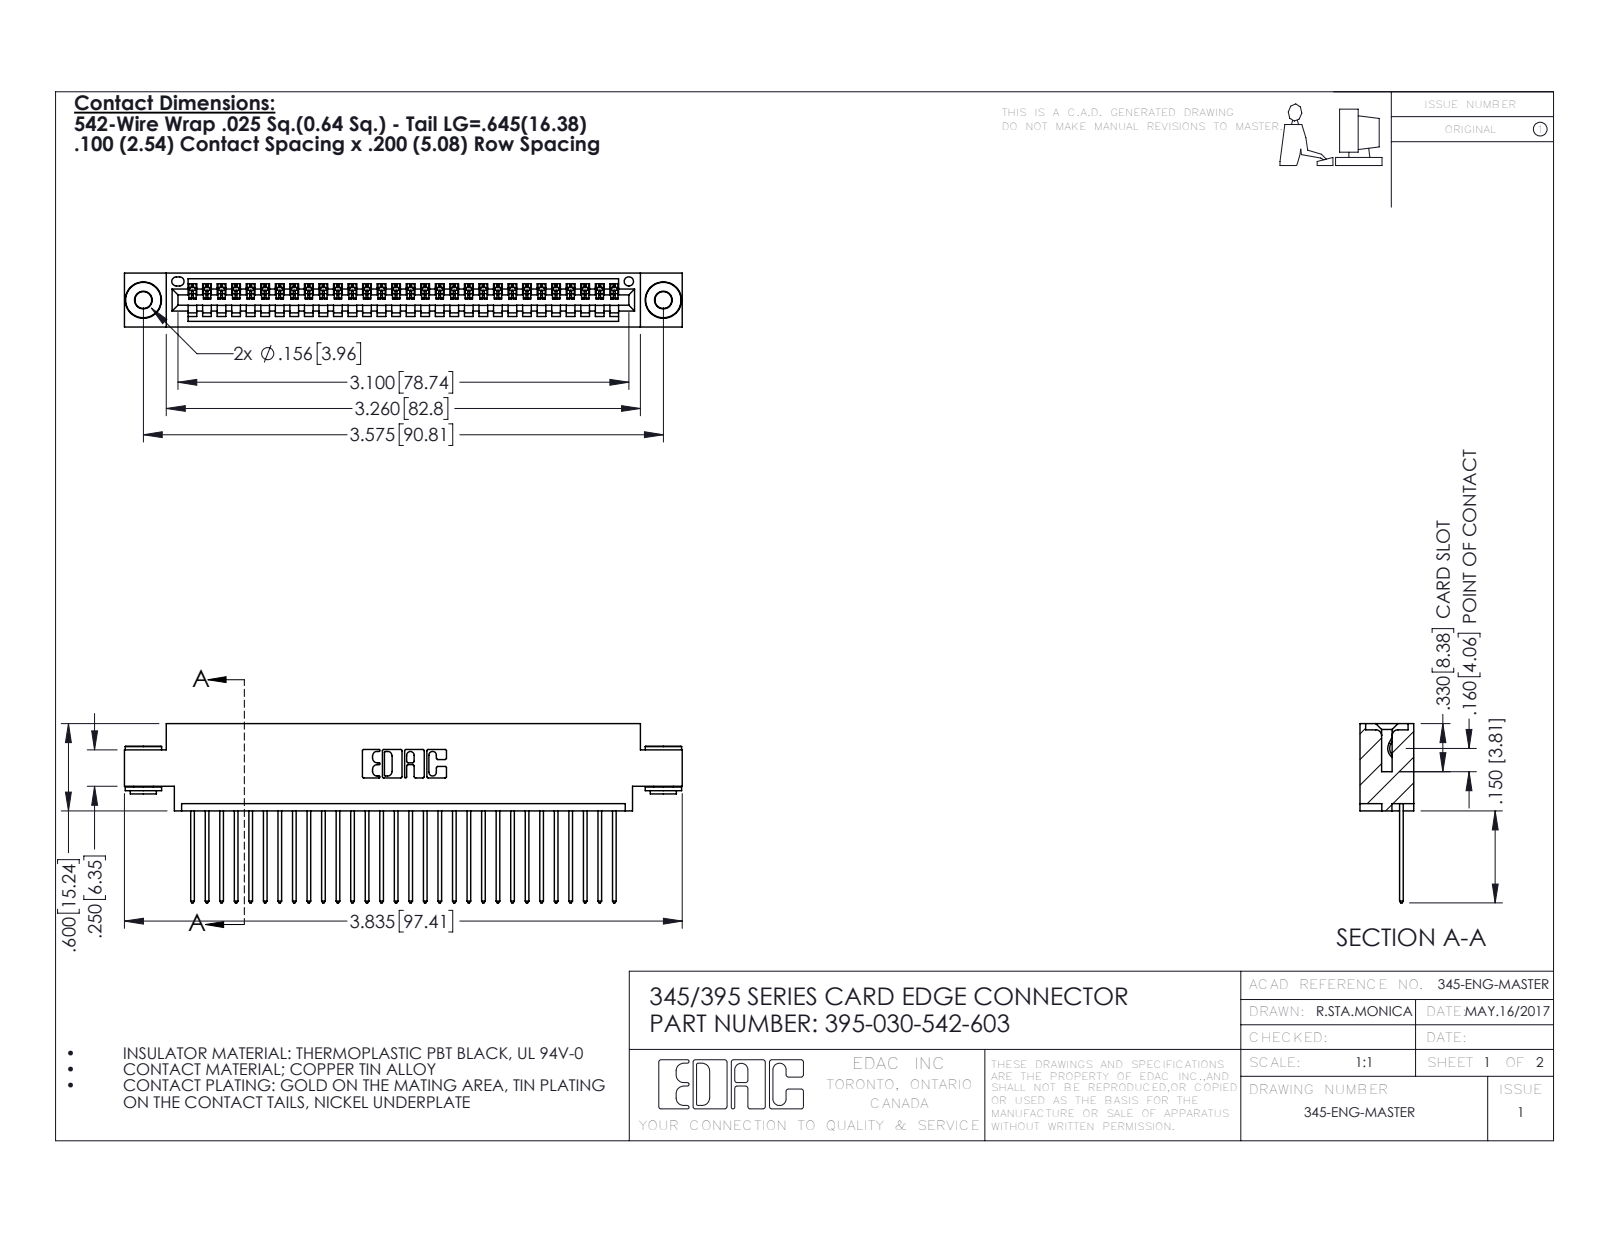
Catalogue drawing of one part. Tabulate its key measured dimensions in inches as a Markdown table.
| quantity | value |
| --- | --- |
| part name | 345-250-002_345-250-002-102; 345 Part_0.170 Offset - 0.156 Dia-TH; 345-292-001_345-293-142; 395-030-542-603 |
| STEP written by | SolidWorks 2016 (CONFIG_CONTROL_DESIGN) |
| units | inches |
| bodies | 33 solids, 1908 faces (1294 planar, 606 cylindrical, 8 other) |
| overall size | 3.835 × 1.232 × 0.37 |
| volume | 0.557 in³ |
| surface area | 19.73 in² |
| round holes (diameter × count) | 0.116 × 2, 0.156 × 2, 0.064 × 1 |
| round bosses / shafts (diameter × count) | 0.25 × 2, 0.18 × 2, 0.136 × 2 |
| partial cylindrical surfaces (radius × count) | 0.006 × 60, 0.01 × 60, 0.01 × 22, 0.007 × 6, 0.031 × 6, 0.026 × 3, 0.031 × 2, 0.04 × 2 |
| main face-to-face distances | 0.072, 0.298, 0.37, 0.098, 0.272, 0.025, 0.2, 0.225, 0.175, 0.149 |
| hole center spacings | 0.27, 3.34, 3.575 |
